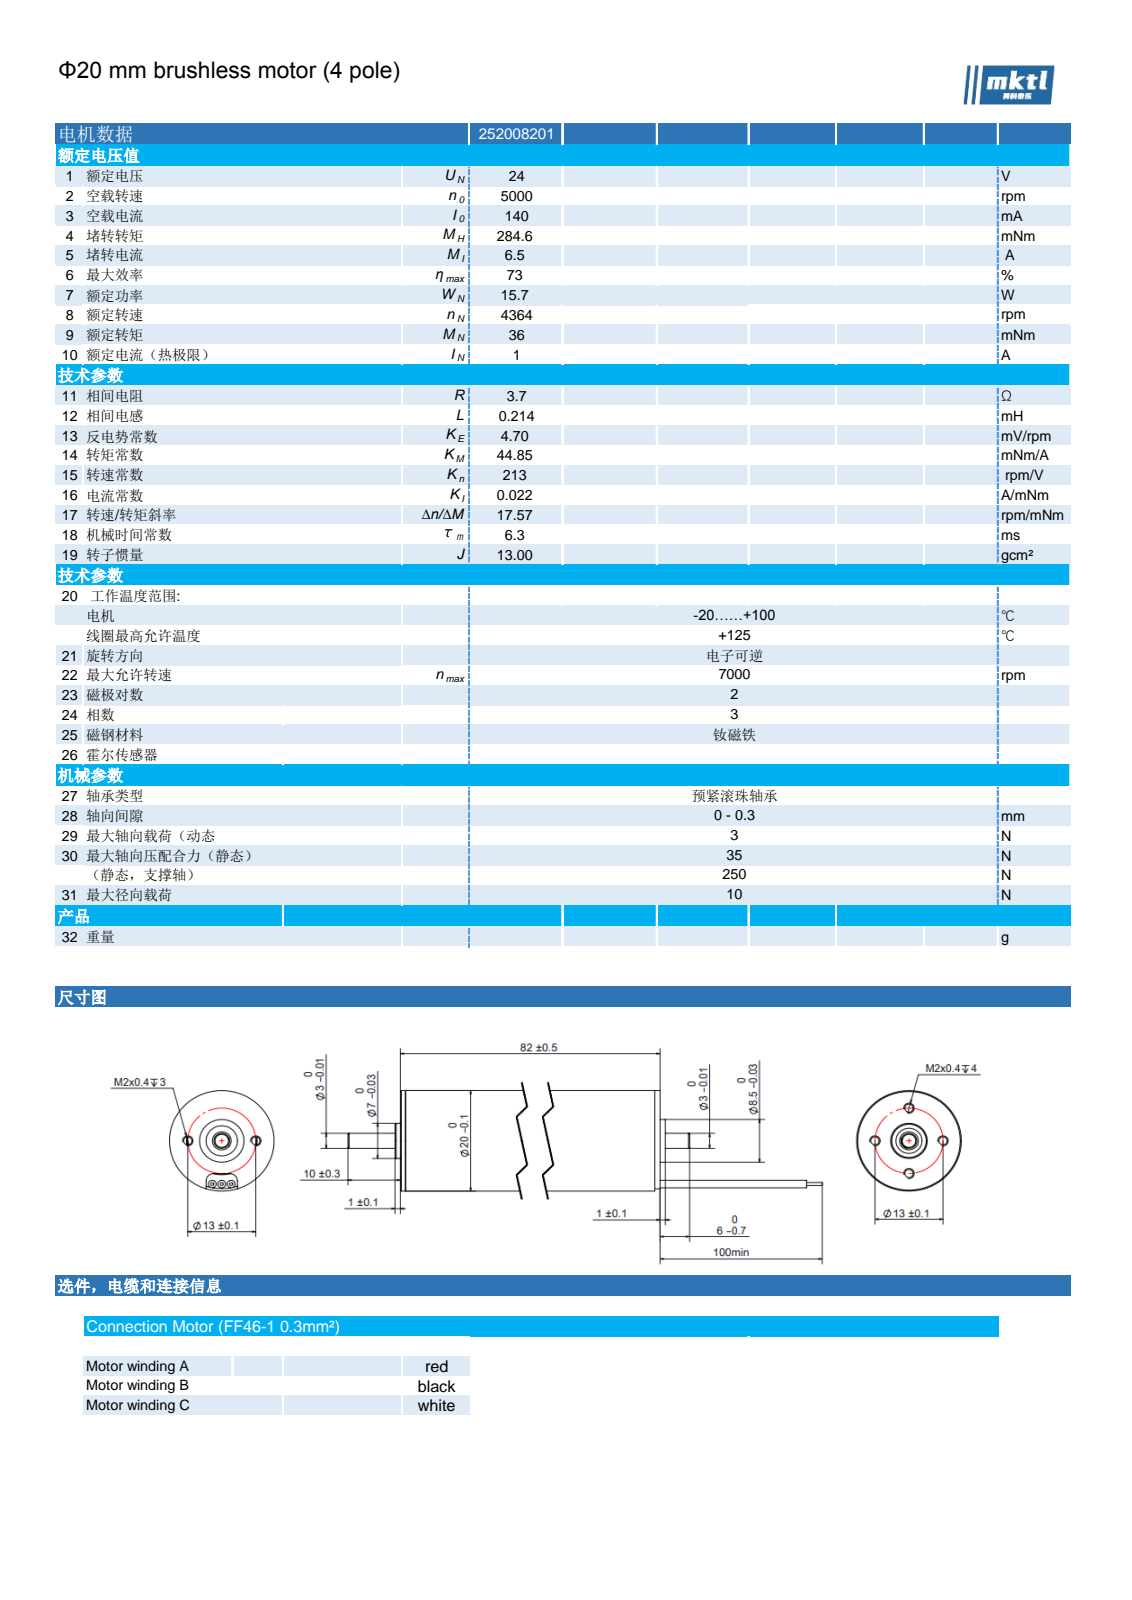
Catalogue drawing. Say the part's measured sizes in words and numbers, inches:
The part is named "252008201". Its 3-D file was written by "SolidWorks 2025 (AUTOMOTIVE_DESIGN)". It is 359 solids with 2304 faces: 753 planar, 1496 cylindrical and 55 other. Overall it measures 4.843 by 0.787 by 0.787 inches. Its volume is 1.415 cubic inches and its surface area 127.9 square inches. Round holes: 6 of diameter 0.063, 3 of diameter 0.02, 1 of diameter 0.118, 1 of diameter 0.236, 1 of diameter 0.315, 1 of diameter 0.406, 1 of diameter 0.516, 1 of diameter 0.531, 1 of diameter 0.65, 1 of diameter 0.669. Round bosses or shafts: 3 of diameter 0.059, 3 of diameter 0.036, 3 of diameter 0.024, 1 of diameter 0.787, 1 of diameter 0.748, 1 of diameter 0.744, 1 of diameter 0.63, 1 of diameter 0.492. Partial cylindrical surfaces (rounded edges, fillets, slot ends): 2 of radius 0.059. The main face-to-face distances are 0.016, 0.039, 0.024, 0.031, 0.197, 3.031, 0.079, 0.047, 0.098, 2.579. The hole center spacings are 0.256, 0.362, 0.443, 0.071, 0.109, 0.132, 0.259, 0.306.
